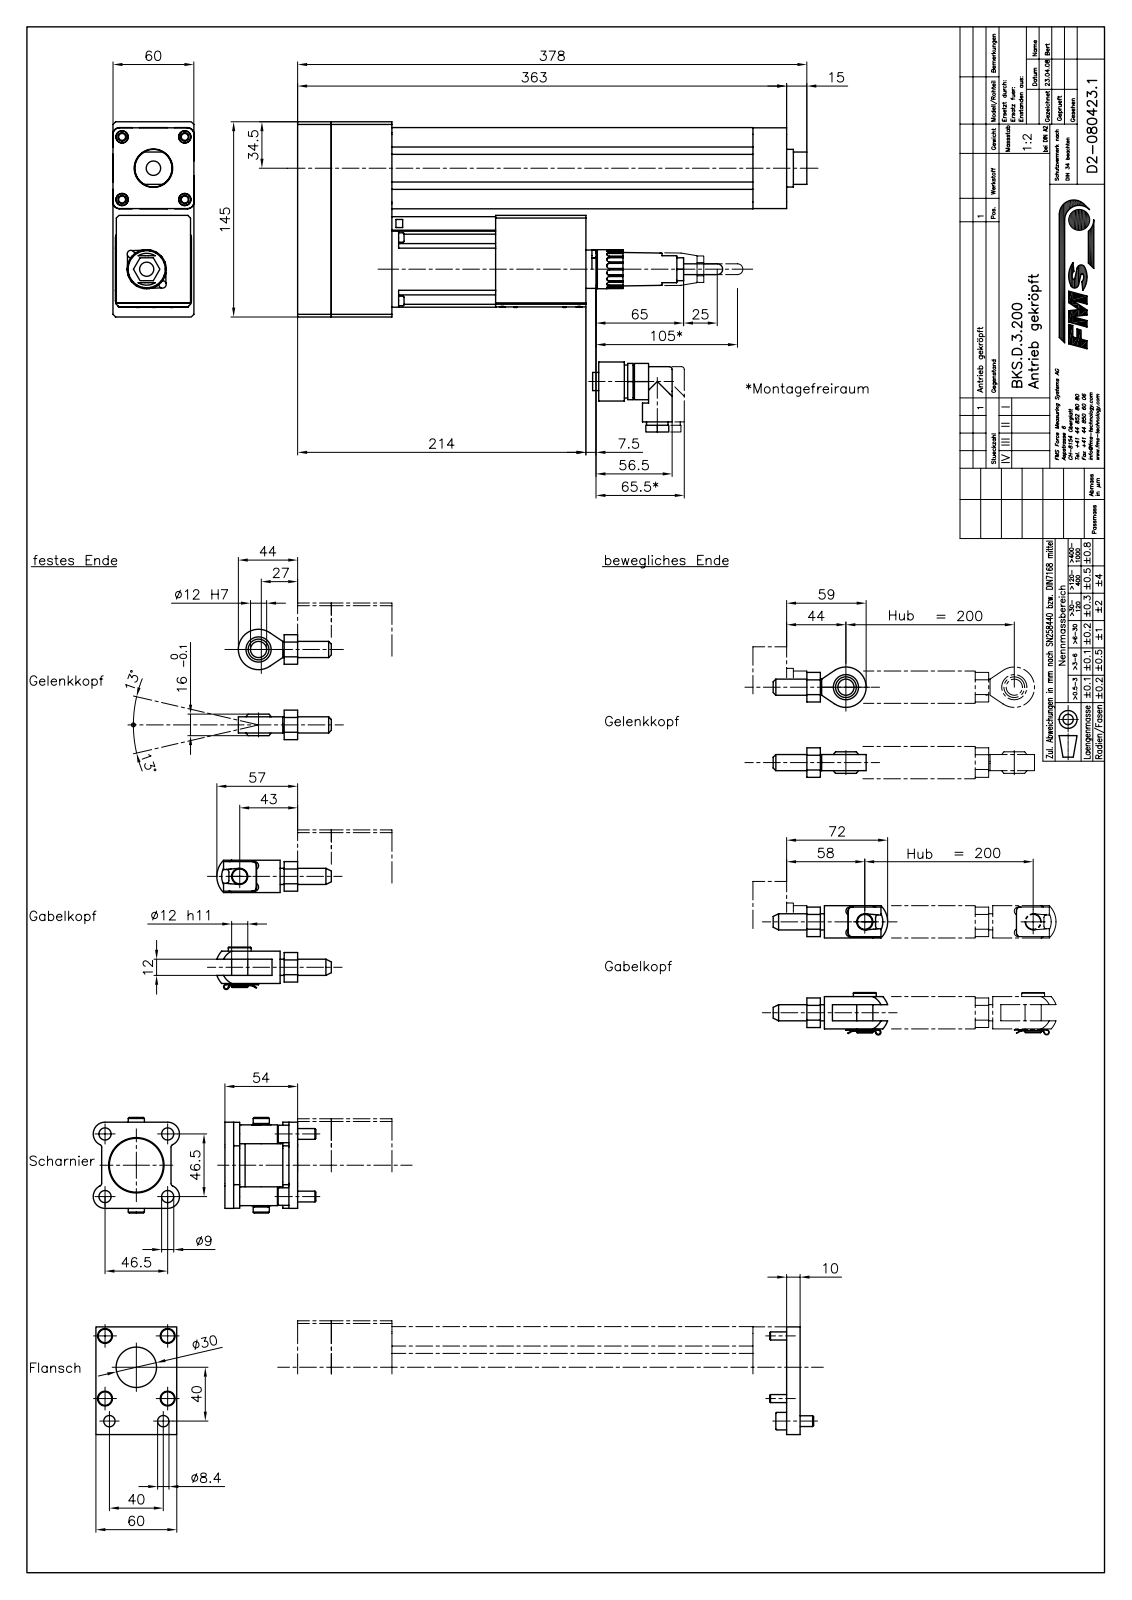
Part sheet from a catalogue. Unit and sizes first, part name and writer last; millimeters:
Units: millimetres
Overall size (bounding box): 466 × 145 × 60.3
Round holes (diameter × count): ⌀2.6 ×10, ⌀3.4 ×8, ⌀5.15 ×8, ⌀3.42 ×6, ⌀5 ×4, ⌀6.3 ×4, ⌀6.4 ×4, ⌀6.65 ×4, ⌀6.91 ×4, ⌀9 ×4, ⌀2.14 ×3, ⌀2.8 ×3
Round bosses / shafts (diameter × count): ⌀3 ×10, ⌀6 ×8, ⌀5.5 ×8, ⌀2.15 ×7, ⌀10 ×5, ⌀7 ×4, ⌀4 ×4, ⌀5 ×3
Partial cylindrical surfaces — rounded edges, fillets, slot ends (radius × count): R2 ×21, R0.5 ×14, R5 ×14, R20 ×8, R4.5 ×4, R5.5 ×4, R8 ×4, R3 ×2
Main face-to-face distances: 60.15, 60.3, 55, 25, 60, 2.65, 70, 5.3, 45, 57.65
Hole centre spacings: 12.41, 22.47, 32.88, 33.3, 35.84, 37.01, 44.09, 46.5
Volume: 1 298 000 mm³ · Surface area: 414 062 mm²
Bodies: 48 solids, 1366 faces (673 planar, 465 cylindrical, 228 other)
Part name (STEP PRODUCT): K0804231; K0803111; K0702222; K0804232 (+8 more)
STEP written by: Mechanical Desktop 2009 (CONFIG_CONTROL_DESIGN)
